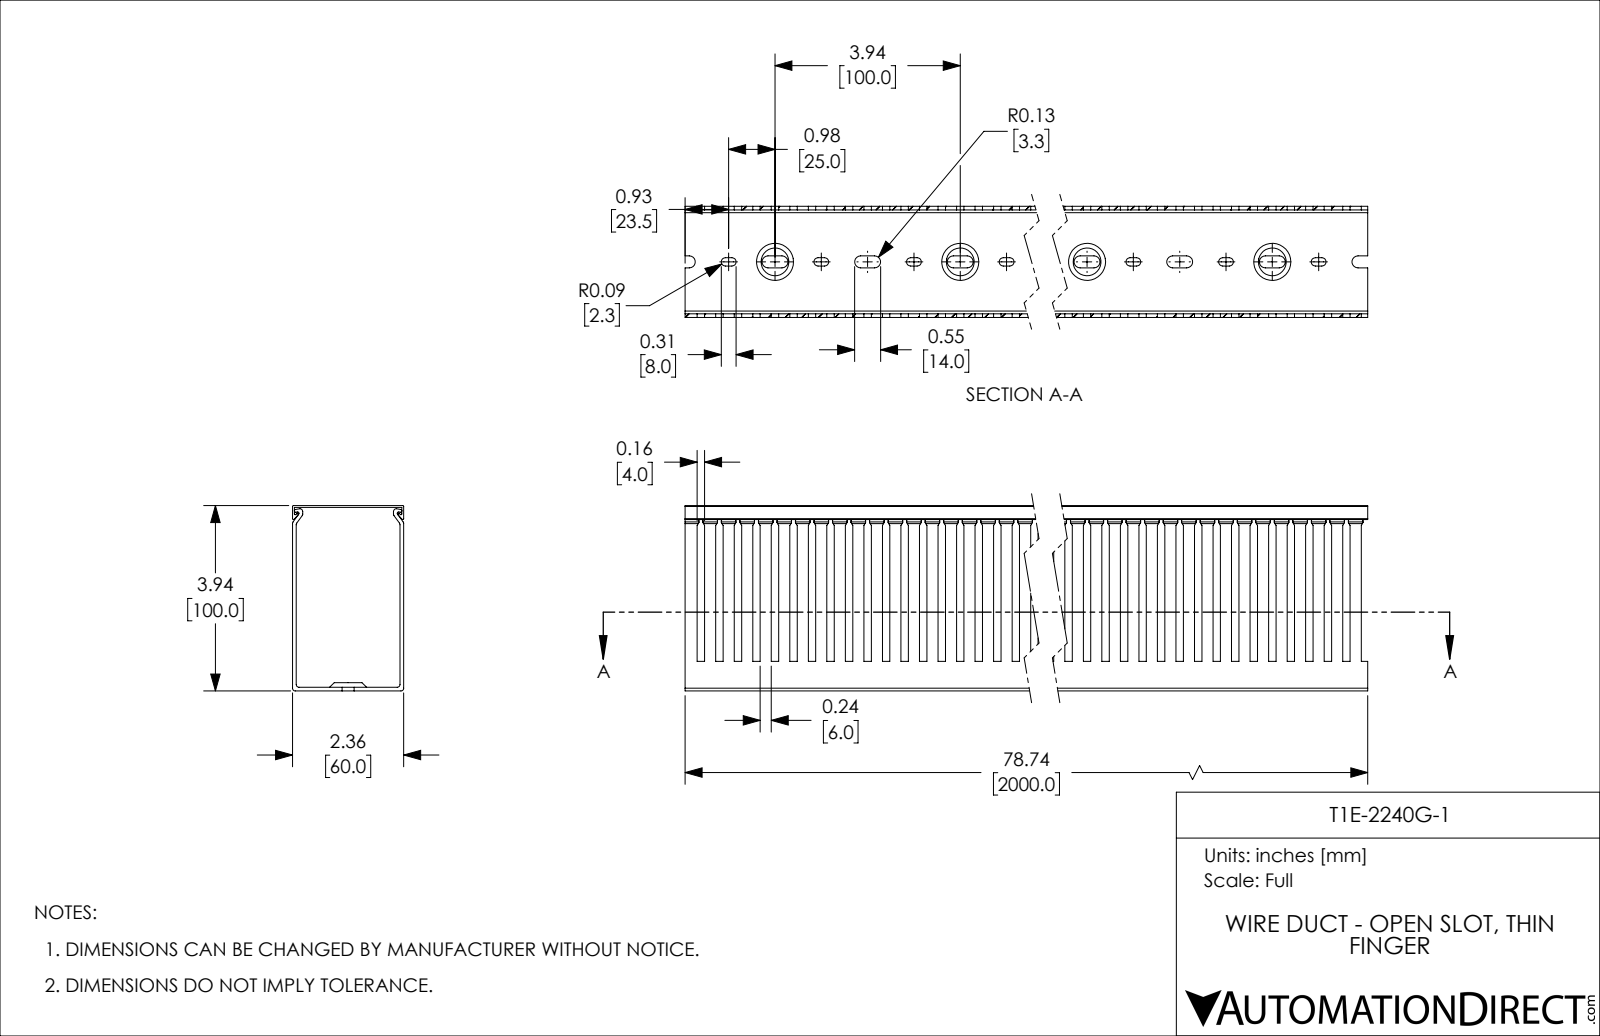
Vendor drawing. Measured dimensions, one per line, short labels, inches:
name: T1E-2240G-1
written by: SolidWorks 2021 (CONFIG_CONTROL_DESIGN)
unit: in
bodies: 2 solids, 1005 faces (534 planar, 431 cylindrical, 40 other)
size: 78.74 × 3.937 × 2.362
volume: 71.76 in³; area: 2 071 in²
rounds: 80× R0.089, 80× R0.128, 12× R0.059, 8× R0.02, 6× R0.03
face distances: 0.079, 2.283, 2.362, 2.205, 0.039, 3.898, 3.937, 3.819, 3.858, 2.323
